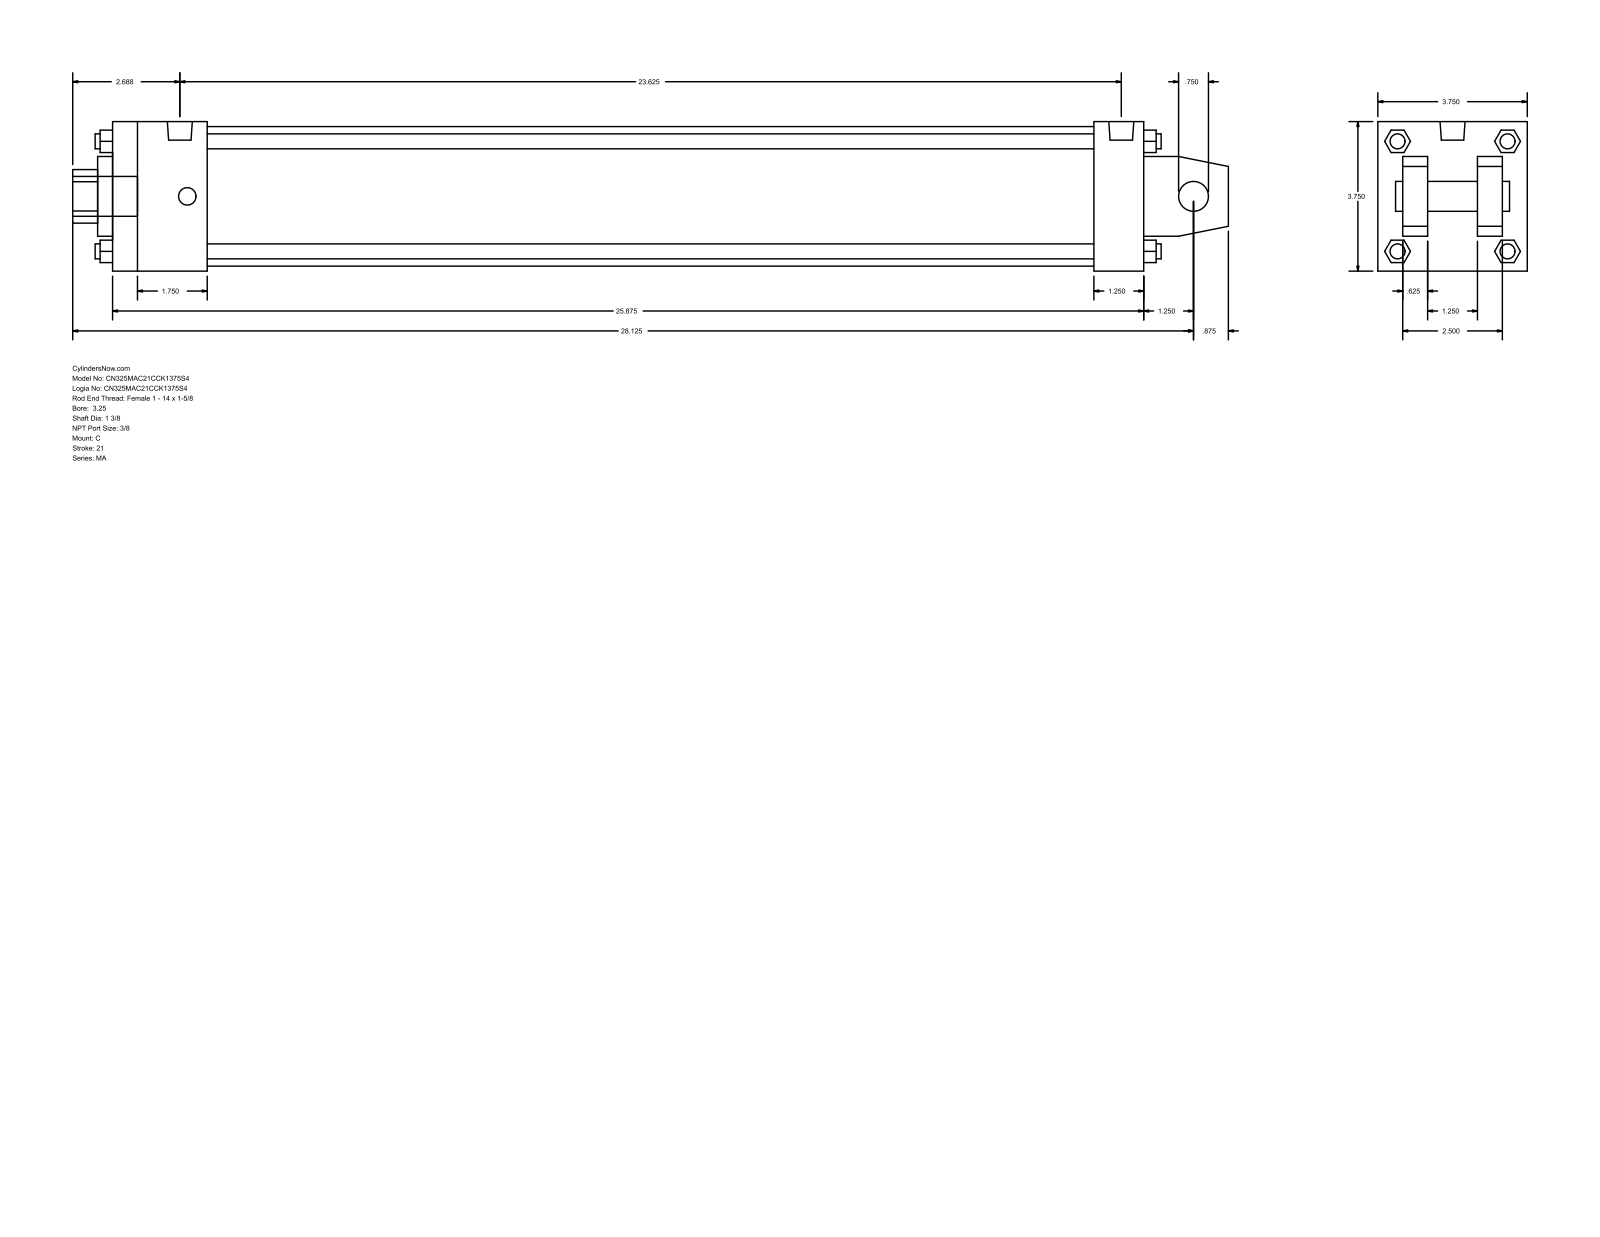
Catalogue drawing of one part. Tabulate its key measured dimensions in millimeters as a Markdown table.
| quantity | value |
| --- | --- |
| part name | MA_C__0325_1.375 |
| STEP written by | GSSL Pune (CONFIG_CONTROL_DESIGN) |
| units | millimeters |
| bodies | 0 solids, 139 faces (108 planar, 31 cylindrical, 0 other) |
| overall size | 736.6 × 95.25 × 95.25 |
| round holes (diameter × count) | 19.05 × 1, 34.92 × 1, 50.8 × 1, 88.9 × 1 |
| round bosses / shafts (diameter × count) | 11.11 × 4, 9.53 × 4, 15.93 × 2, 25.4 × 1 |
| partial cylindrical surfaces (radius × count) | 17.06 × 1 |
| main face-to-face distances | 95.24, 15.87, 31.74, 63.5, 657.22, 79.37, 47.63, 625.48, 60.32, 565.16 |
